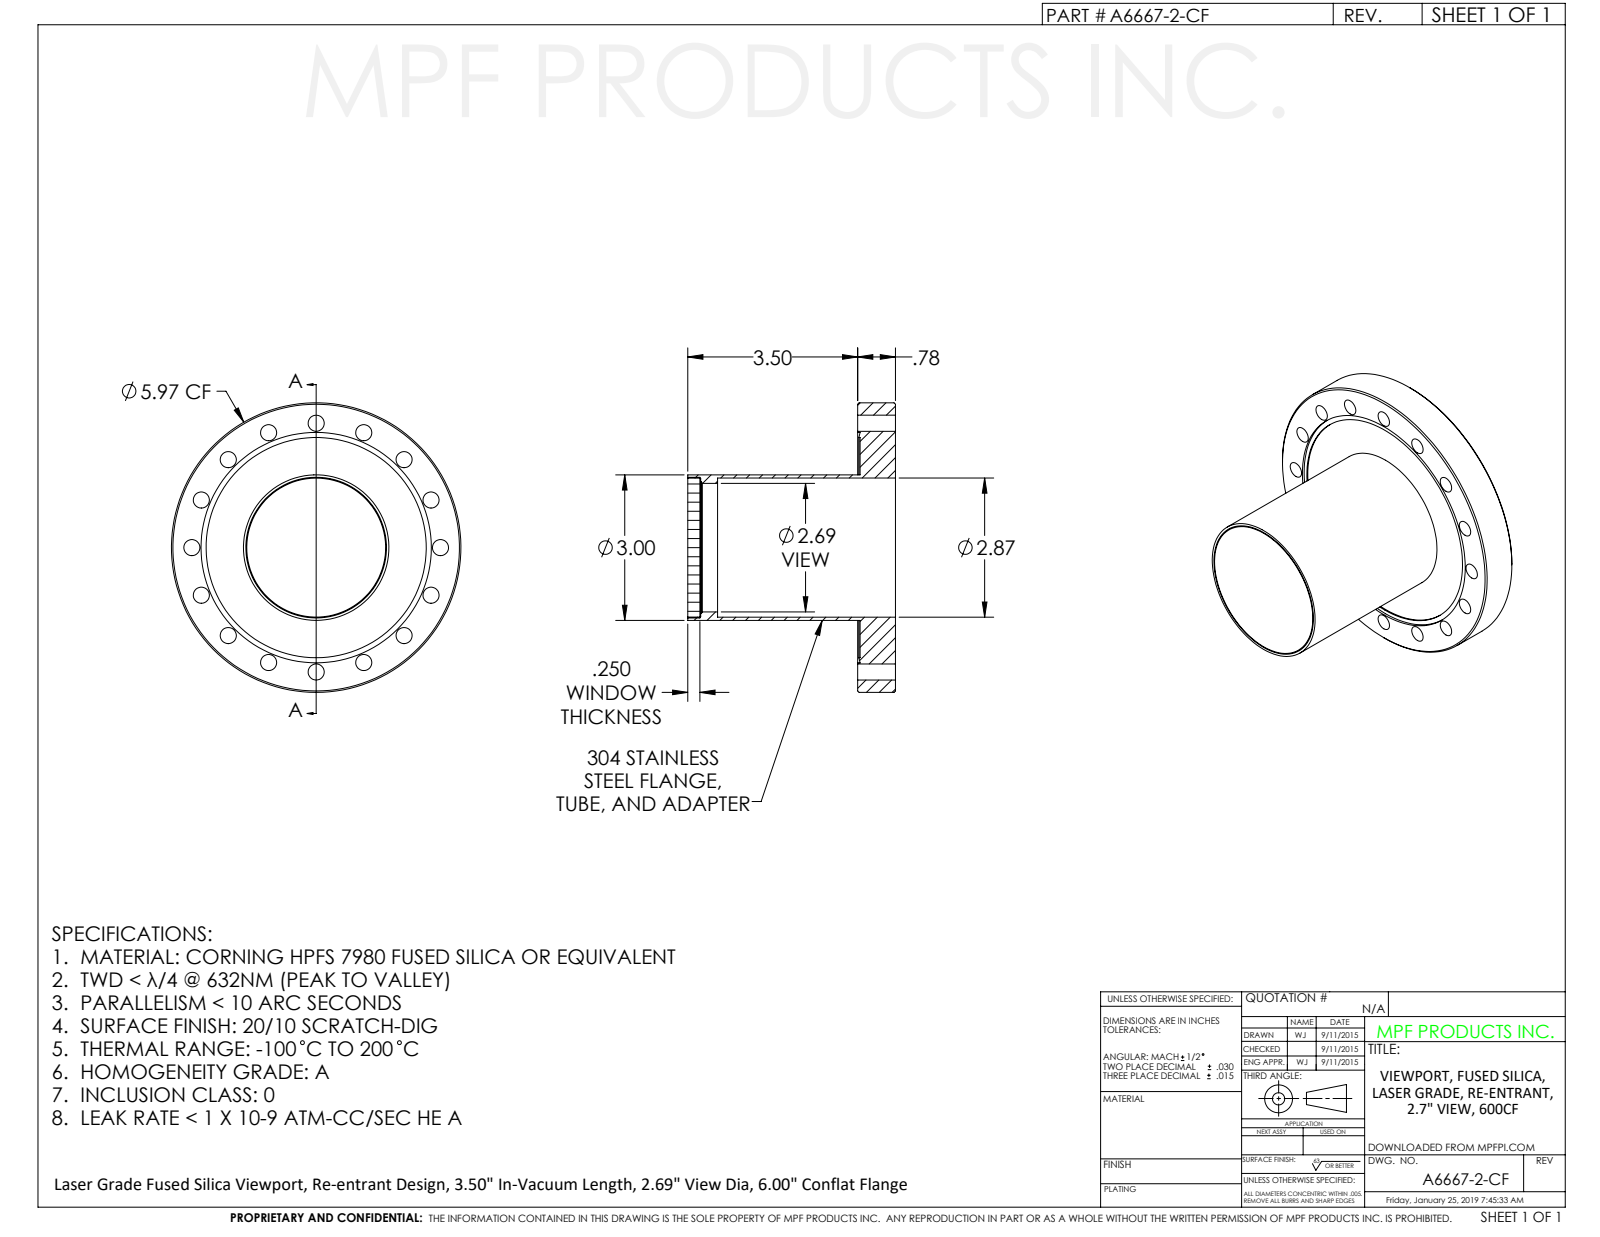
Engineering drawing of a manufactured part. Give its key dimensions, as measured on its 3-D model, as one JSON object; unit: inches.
{"part_name": "A6667-2-CF", "step_written_by": "SolidWorks 2011 (CONFIG_CONTROL_DESIGN)", "units": "inches", "bodies": {"solids": 1, "faces": 97, "planar": 17, "cylindrical": 66, "other": 14}, "overall_size": [6, 6, 4.279], "volume_in3": 19.03, "surface_area_in2": 168.3, "round_holes": [[0.332, 16], [2.69, 1], [2.735, 1], [2.865, 1], [2.87, 1], [2.96, 1], [3, 1], [4.54, 1], [4.75, 1]], "round_bosses_or_shafts": [[6, 1], [2.995, 1], [2.905, 1], [2.785, 1], [2.73, 1]], "face_to_face_distances": [0.729, 0.78, 0.051, 4.279, 3.55, 3.499, 4.029, 3.3, 3.249, 0.25], "hole_center_spacings": [1, 4.264, 4.738, 5.03, 1.963, 2.564, 3.626, 2.849]}
